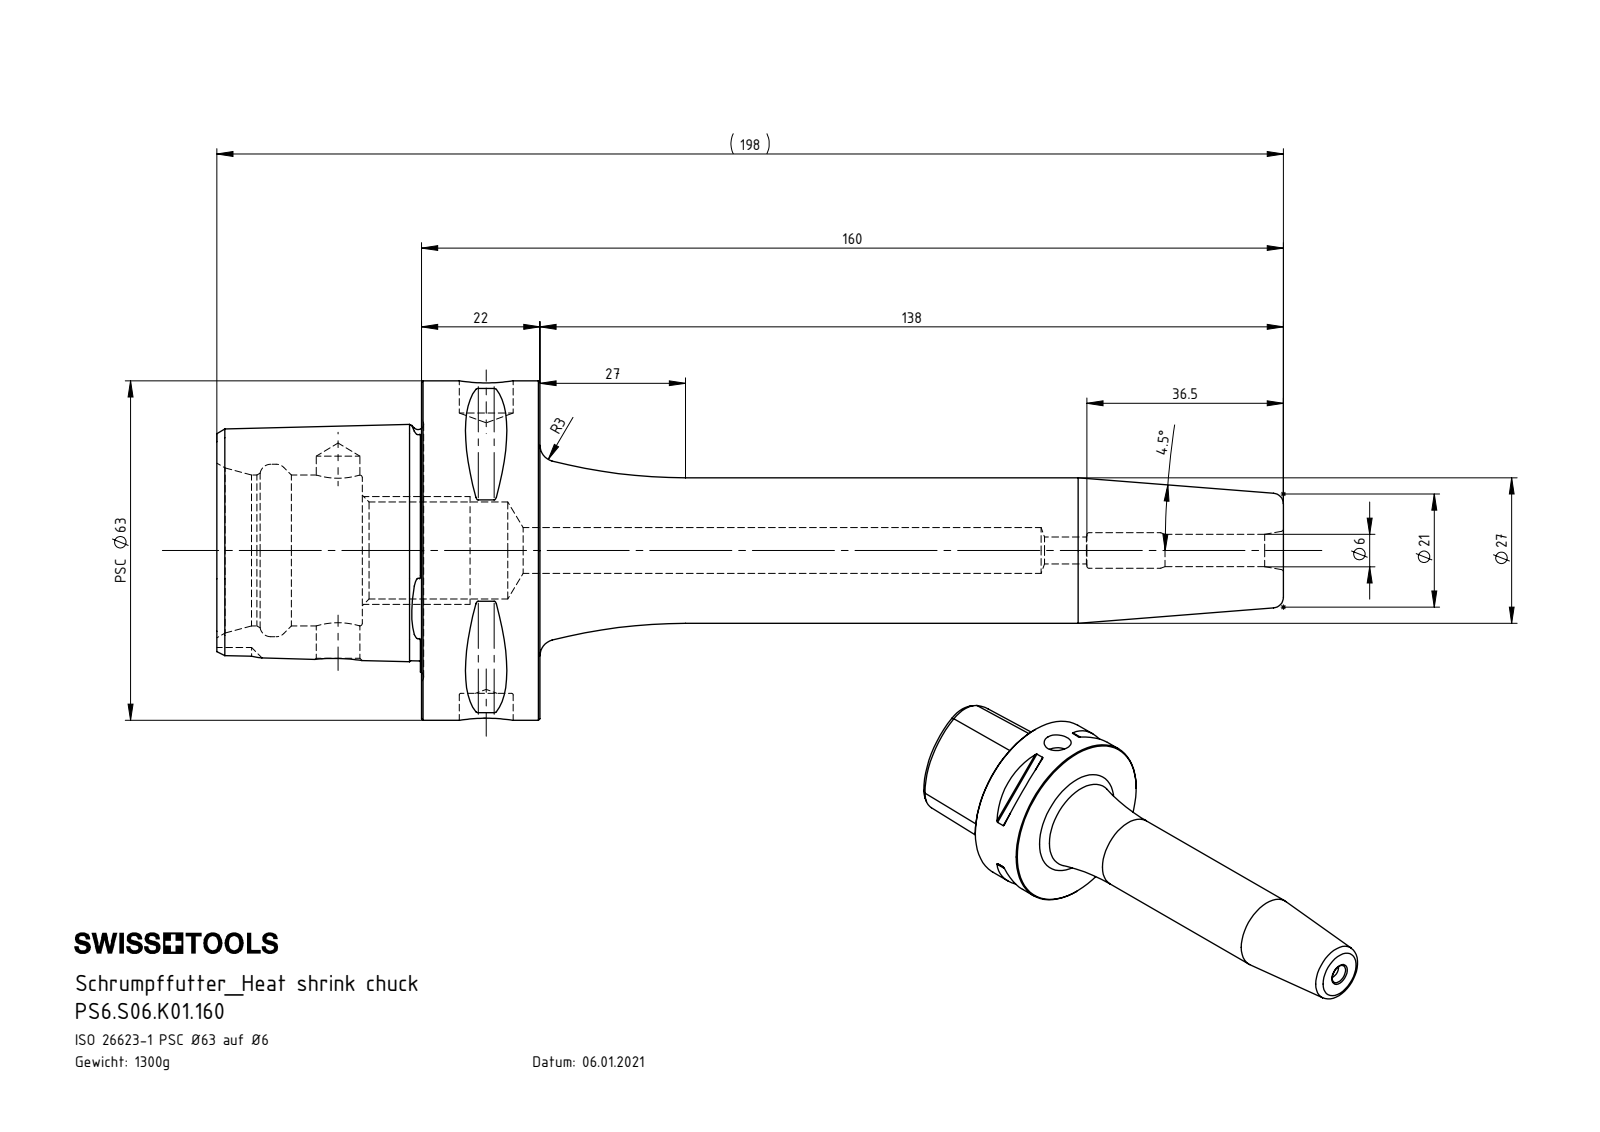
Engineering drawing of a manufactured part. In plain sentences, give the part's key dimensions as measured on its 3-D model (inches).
The part is named "PS6.S06.K01.160". Its 3-D file was written by "SolidWorks 2022 (AUTOMOTIVE_DESIGN)". It is 1 solid with 158 faces: 22 planar, 37 cylindrical and 99 other. Overall it measures 7.795 by 2.48 by 2.48 inches. Its volume is 10.11 cubic inches and its surface area 53.55 square inches. Round holes: 1 of diameter 0.197, 1 of diameter 0.236, 1 of diameter 0.26, 1 of diameter 0.319, 1 of diameter 0.335, 1 of diameter 0.394, 1 of diameter 0.709, 1 of diameter 1.102, 1 of diameter 1.26. Round bosses or shafts: 1 of diameter 2.48, 1 of diameter 1.063. Partial cylindrical surfaces (rounded edges, fillets, slot ends): 8 of radius 0.02, 1 of radius 0.236. The main face-to-face distances are 0.866, 1.496, 2.362, 0.98, 1.063, 0.433, 1.299, 7.795, 6.732, 6.299. The hole center spacings are 1.083.
